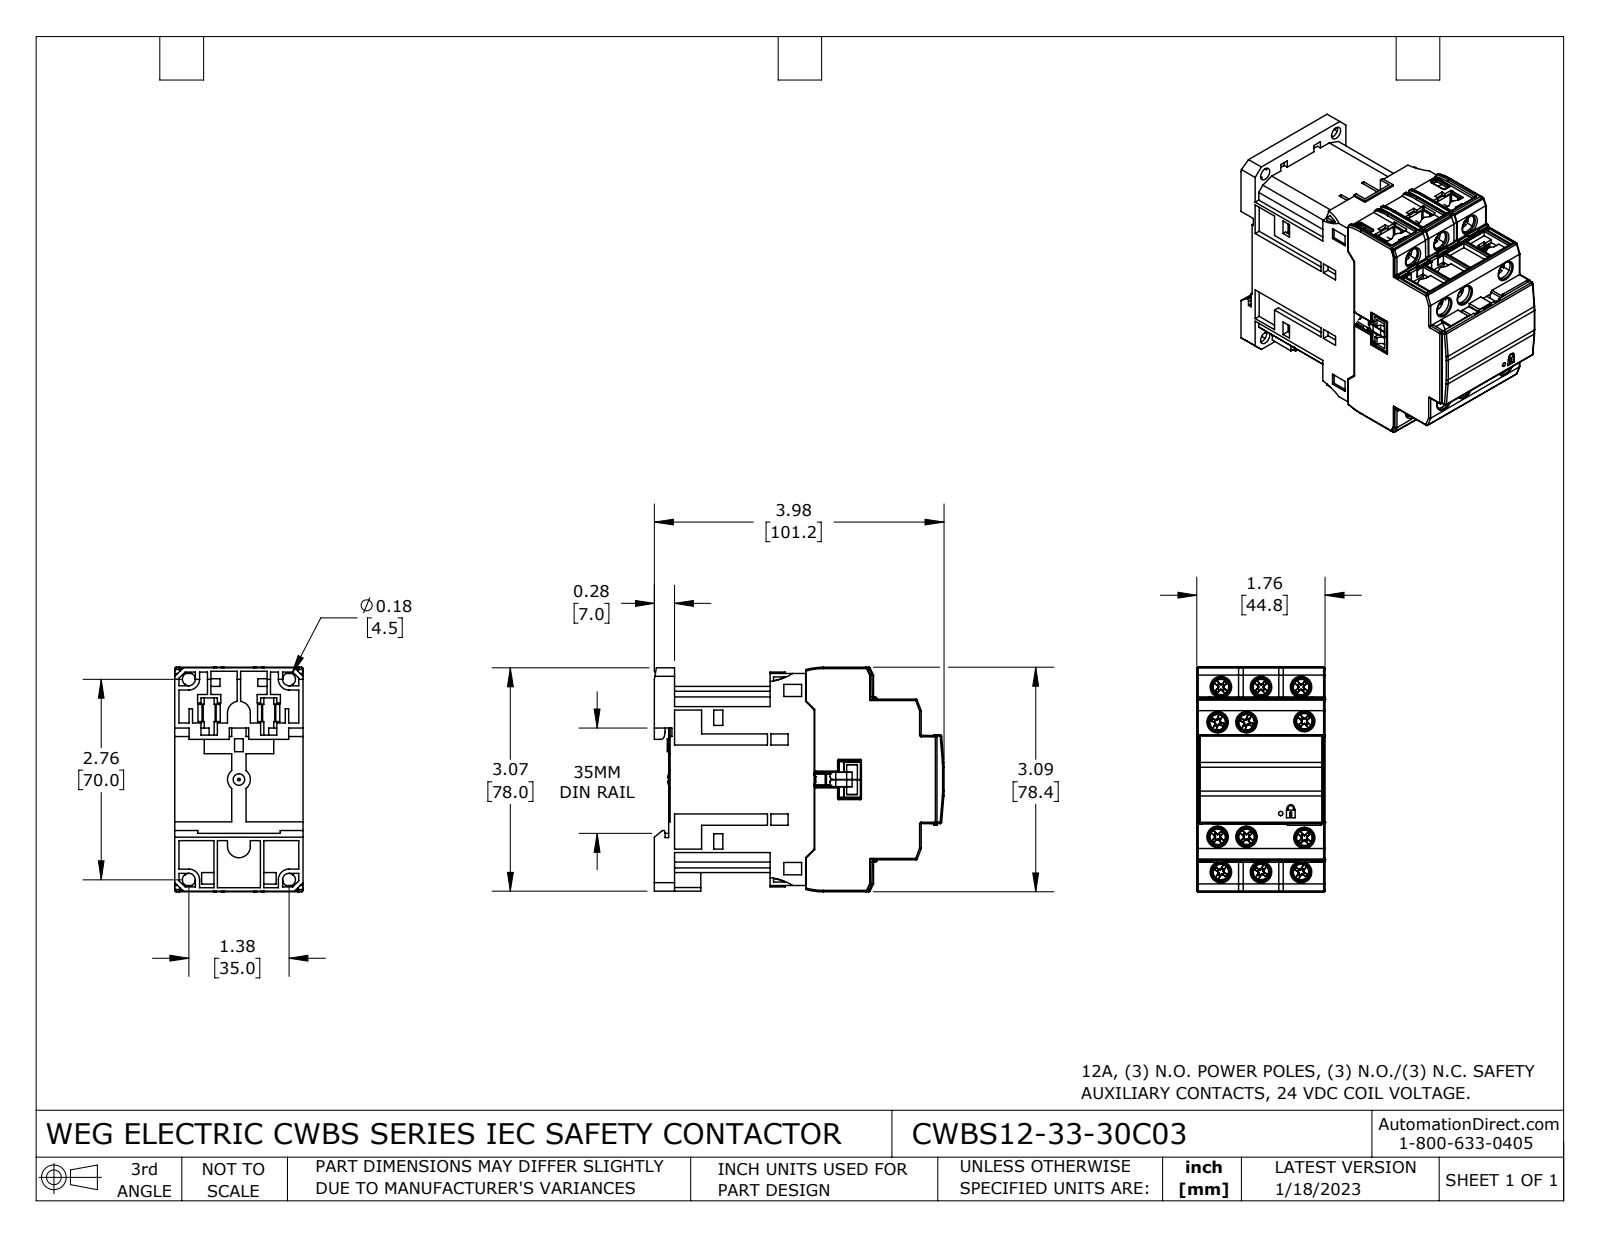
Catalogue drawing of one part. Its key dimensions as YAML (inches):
part_name: "CWBS12-33-30C03"
step_written_by: "SolidWorks 2021 (CONFIG_CONTROL_DESIGN)"
units: inches
bodies: {solids: 45, faces: 3244, planar: 2306, cylindrical: 594, other: 344}
overall_size: [3.982, 3.087, 1.764]
volume: 15.16
surface_area: 128.7
round_holes:
  - {diameter: 0.124, count: 12}
  - {diameter: 0.256, count: 6}
  - {diameter: 0.177, count: 4}
  - {diameter: 0.236, count: 2}
  - {diameter: 0.059, count: 1}
round_bosses_or_shafts:
  - {diameter: 0.169, count: 12}
  - {diameter: 0.138, count: 12}
  - {diameter: 0.107, count: 8}
  - {diameter: 0.107, count: 4}
partial_cylinders:
  - {radius: 0.02, count: 134}
  - {radius: 0.012, count: 52}
  - {radius: 0.071, count: 24}
  - {radius: 0.964, count: 24}
  - {radius: 2.128, count: 24}
  - {radius: 0.016, count: 20}
  - {radius: 0.039, count: 17}
  - {radius: 0.106, count: 11}
face_to_face_distances: [1.764, 0.047, 3.667, 1.717, 1.687, 0.028, 0.157, 1.53, 1.98, 2.138]
hole_center_spacings: [0.551, 1.102, 0.829, 2.396, 0.237, 0.398, 0.584, 0.598]
